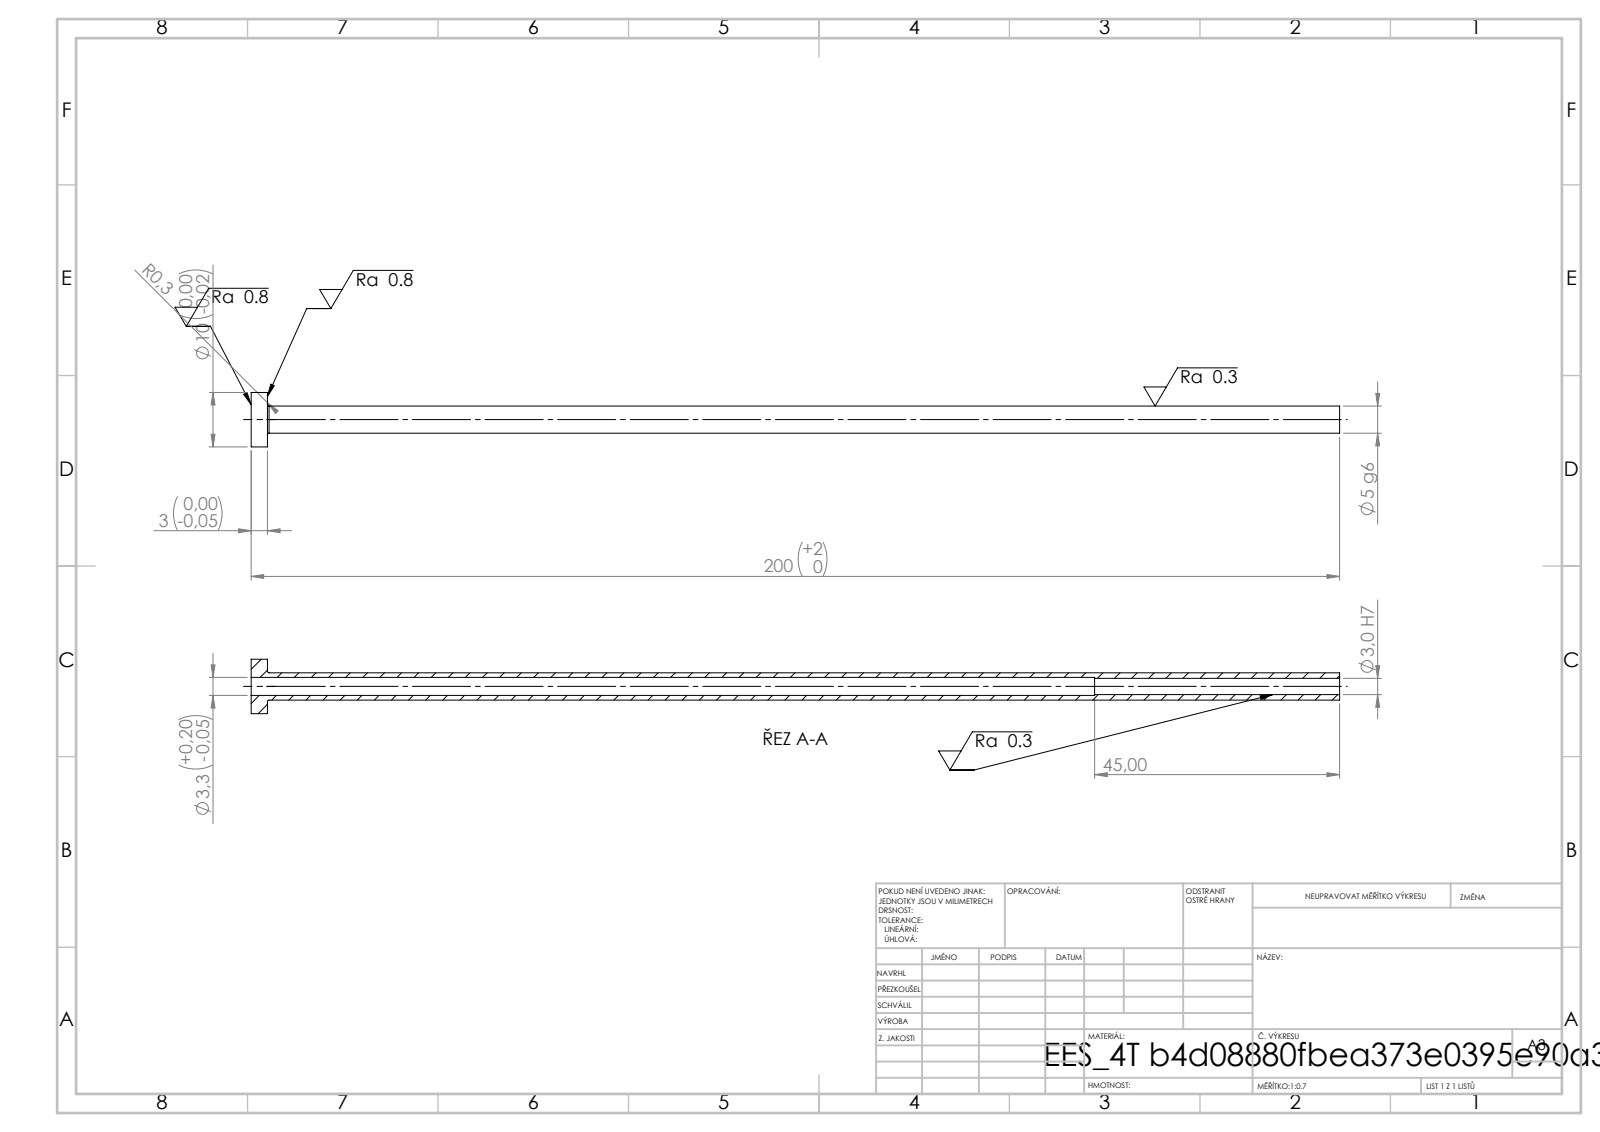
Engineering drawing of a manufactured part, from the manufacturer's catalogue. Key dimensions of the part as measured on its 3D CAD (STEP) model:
STEP written by: SolidWorks 2019 (CONFIG_CONTROL_DESIGN)
Units: millimetres
Bodies: 1 solid, 14 faces (4 planar, 8 cylindrical, 2 other)
Overall size (bounding box): 200 × 10 × 10
Volume: 2 460 mm³ · Surface area: 5 361 mm²
Round holes (diameter × count): ⌀3 ×1, ⌀3.3 ×1
Round bosses / shafts (diameter × count): ⌀10 ×1, ⌀5 ×1
Main face-to-face distances: 3, 200, 197, 155, 152, 45
